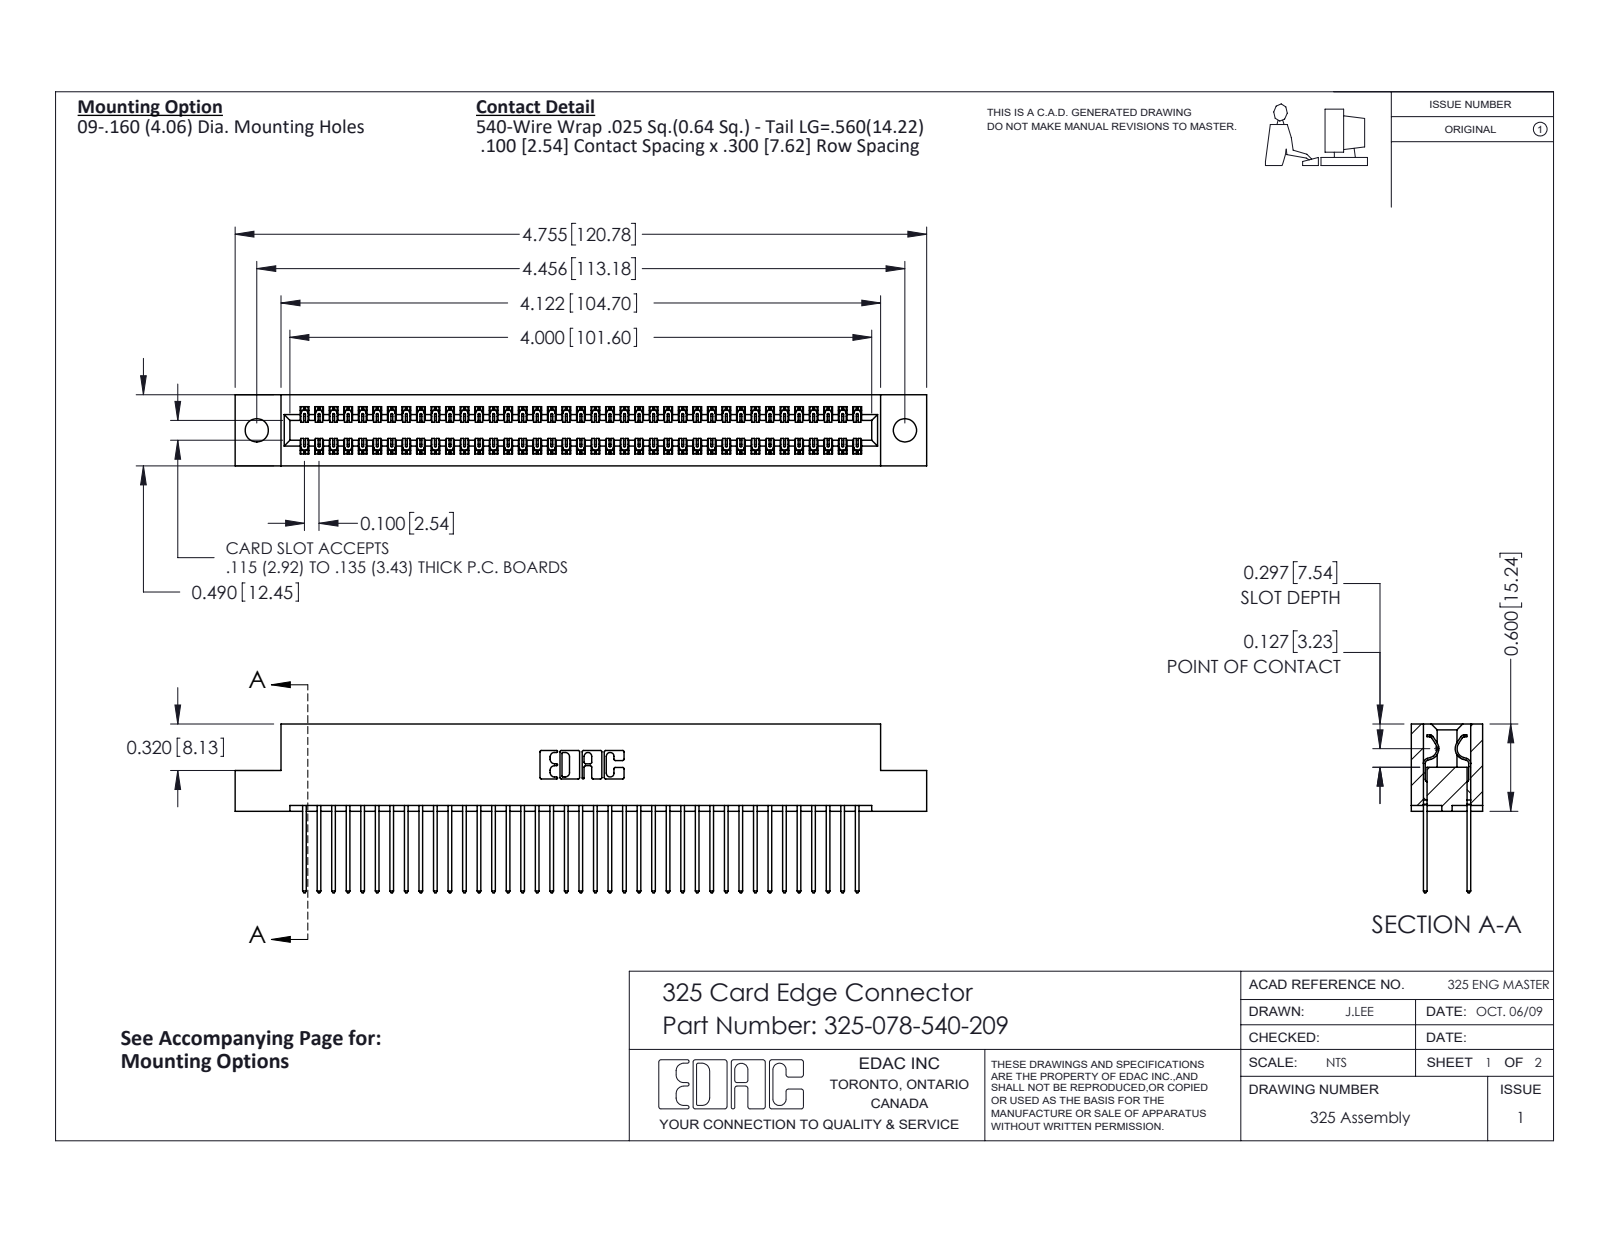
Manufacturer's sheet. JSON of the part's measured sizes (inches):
{"part_name": "325 Part_.160 TH; 325-292-001_325-293-140; 325-078-540-209", "step_written_by": "SolidWorks 2016 (CONFIG_CONTROL_DESIGN)", "units": "inches", "bodies": {"solids": 79, "faces": 4170, "planar": 2878, "cylindrical": 1292, "other": 0}, "overall_size": [4.755, 1.16, 0.49], "volume_in3": 0.954, "surface_area_in2": 31.27, "round_holes": [[0.16, 2]], "partial_cylinders_radius": [[0.006, 117], [0.01, 78], [0.01, 22], [0.007, 6], [0.031, 6], [0.026, 3], [0.014, 2], [0.022, 2]], "face_to_face_distances": [0.083, 0.407, 0.3, 0.107, 0.383, 0.025, 0.49, 0.325, 0.275, 0.56], "hole_center_spacings": [4.456]}
